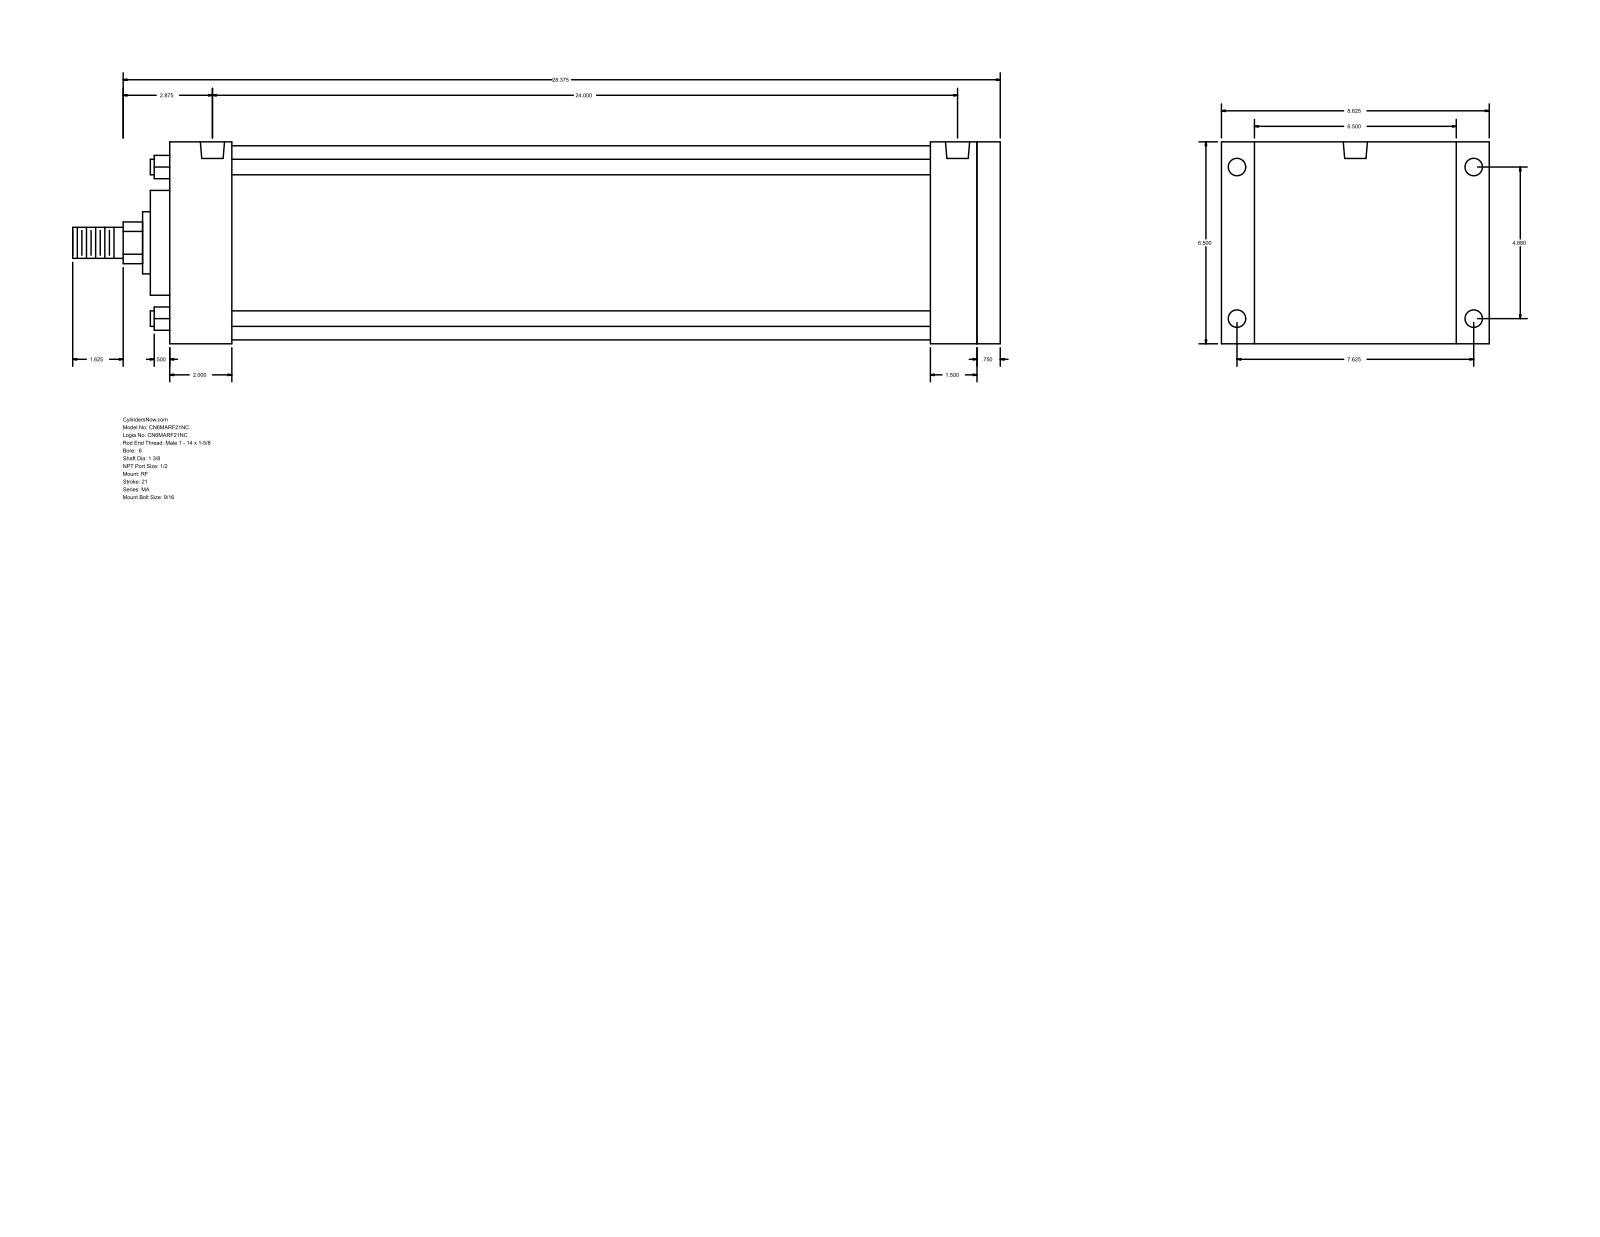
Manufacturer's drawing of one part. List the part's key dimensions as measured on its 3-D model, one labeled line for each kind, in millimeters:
Part name (STEP PRODUCT): MA_RF__0600_1.375
STEP written by: GSSL Pune (CONFIG_CONTROL_DESIGN)
Units: millimetres
Bodies: 0 solids, 94 faces (65 planar, 29 cylindrical, 0 other)
Overall size (bounding box): 762 × 219.07 × 165.1
Round holes (diameter × count): ⌀14.29 ×4, ⌀17.46 ×4, ⌀19.77 ×2
Round bosses / shafts (diameter × count): ⌀12.7 ×4, ⌀158.75 ×1, ⌀85.72 ×1, ⌀50.8 ×1, ⌀34.92 ×1, ⌀25.4 ×1
Partial cylindrical surfaces — rounded edges, fillets, slot ends (radius × count): R17.06 ×1
Main face-to-face distances: 165.1, 682.63, 663.57, 19.06, 57.15, 50.8, 612.77, 631.83, 625.48, 574.68
Hole centre spacings: 123.96, 193.68, 229.95, 612.77, 3.18, 609.59
